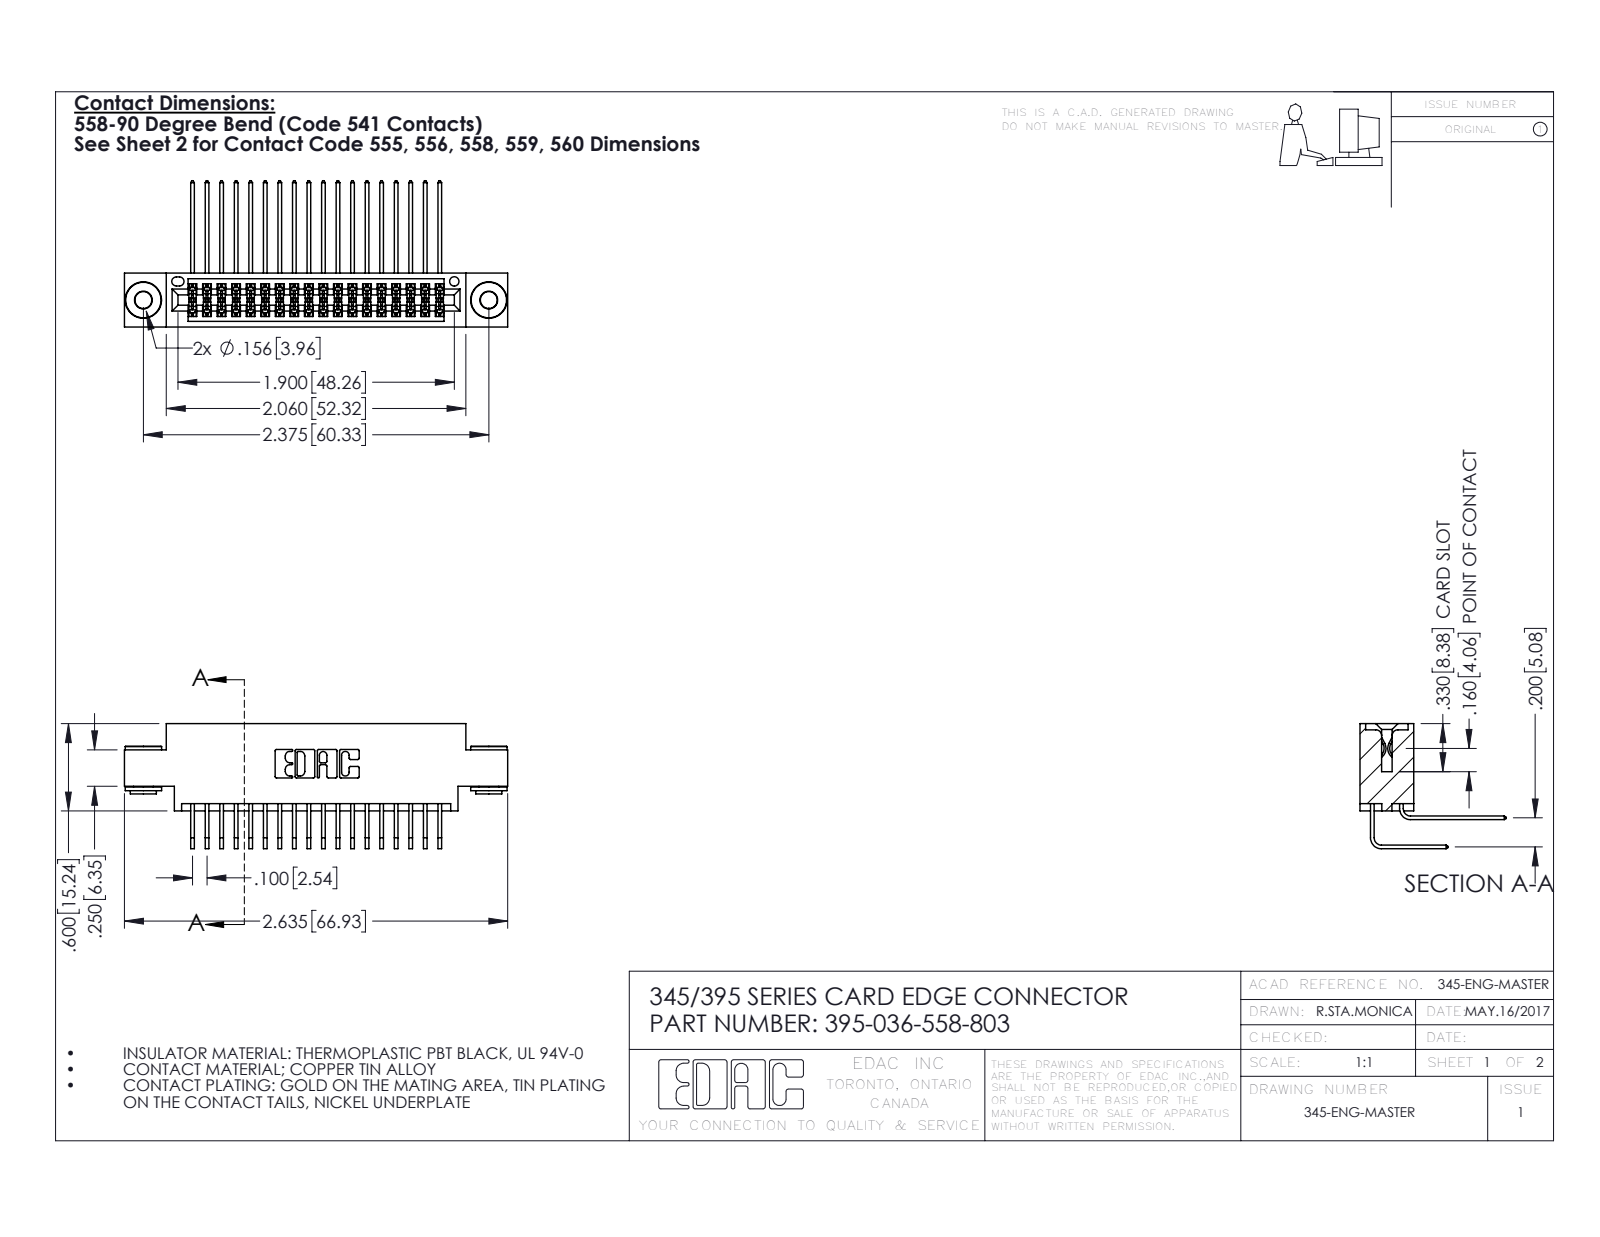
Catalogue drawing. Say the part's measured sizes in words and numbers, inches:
The part is named "345-292-001_558 Tail - 2; 345 Part_0.170 Offset - 0.156 Dia-TH; 345-250-002_345-250-002-102; 395-036-558-803 (+1 more)". Its 3-D file was written by "SolidWorks 2016 (CONFIG_CONTROL_DESIGN)". It is 39 solids with 2040 faces: 1354 planar, 678 cylindrical and 8 other. Overall it measures 2.635 by 1.005 by 0.859 inches. Its volume is 0.39 cubic inches and its surface area 15.98 square inches. Round holes: 2 of diameter 0.116, 2 of diameter 0.156, 1 of diameter 0.064. Round bosses or shafts: 2 of diameter 0.25, 2 of diameter 0.18, 2 of diameter 0.136. Partial cylindrical surfaces (rounded edges, fillets, slot ends): 55 of radius 0.006, 22 of radius 0.01, 6 of radius 0.007, 6 of radius 0.031, 3 of radius 0.026, 2 of radius 0.014, 2 of radius 0.019, 2 of radius 0.022. The main face-to-face distances are 0.2, 0.072, 0.298, 0.37, 0.098, 0.272, 0.025, 0.225, 0.175, 0.025. The hole center spacings are 0.27, 2.141, 2.375.
